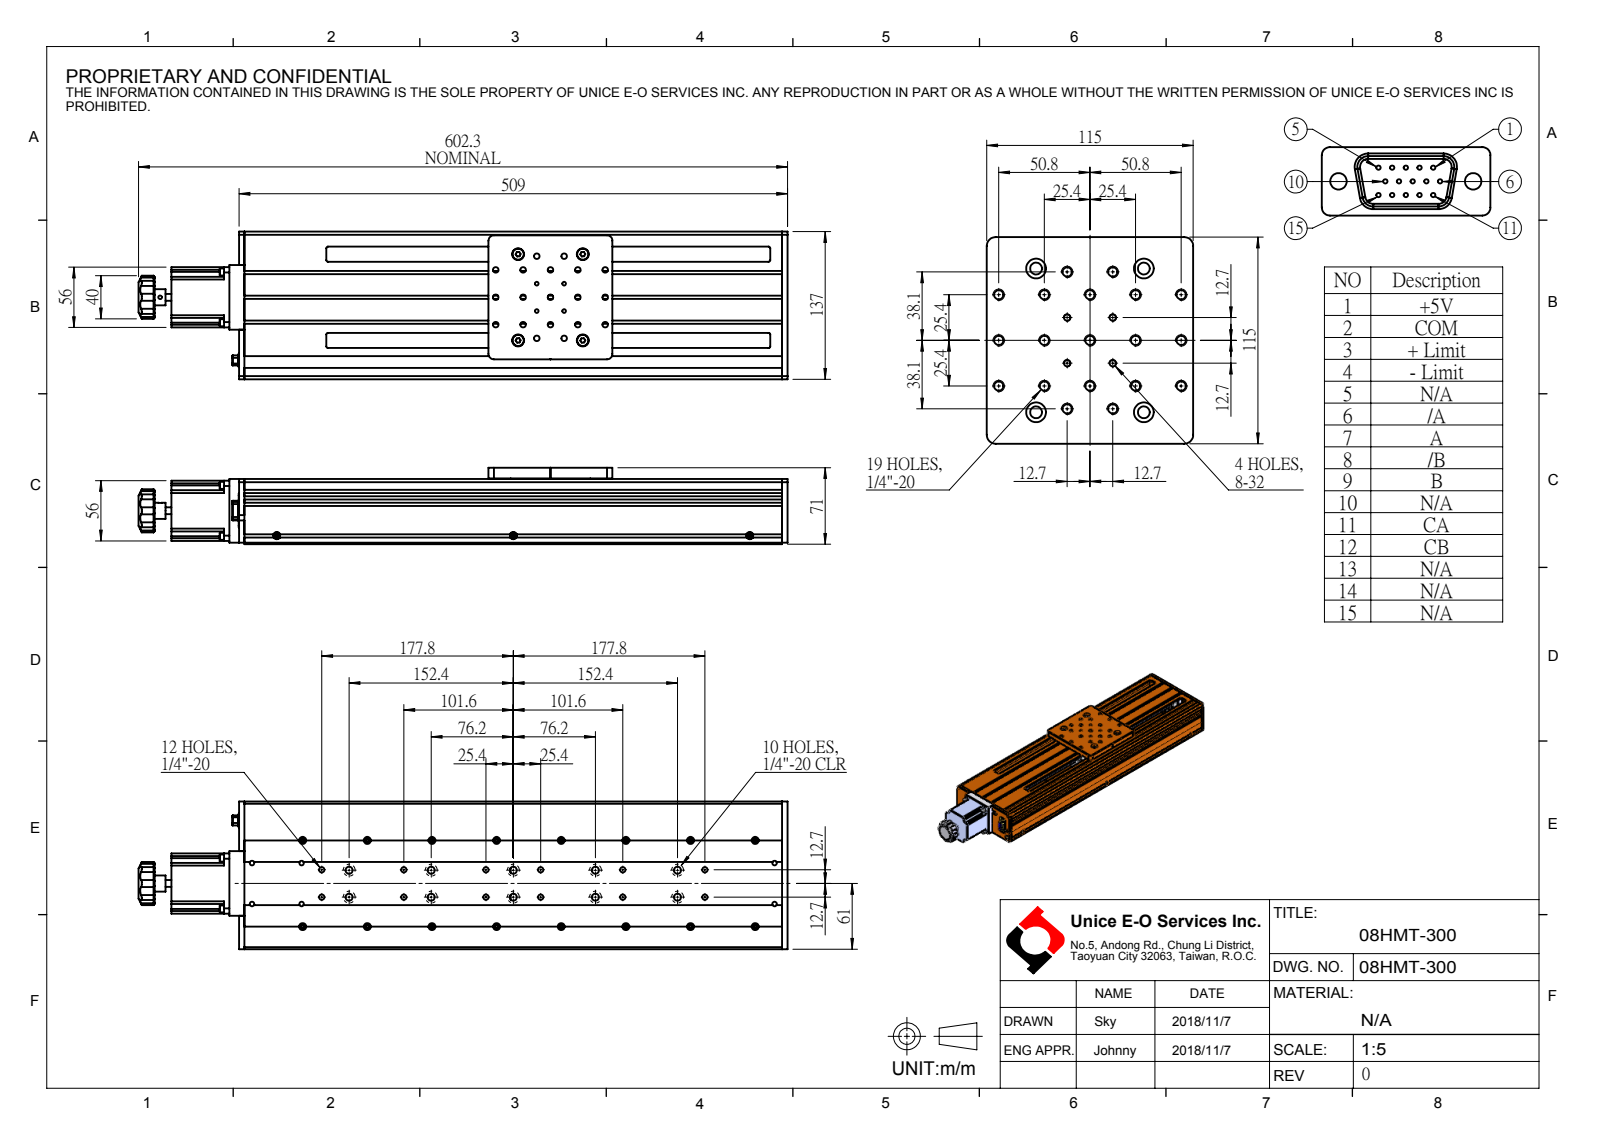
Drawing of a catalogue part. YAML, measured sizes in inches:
part_name: "08HMT-300"
step_written_by: "SolidWorks 2016 (AUTOMOTIVE_DESIGN)"
units: inches
bodies: {solids: 0, faces: 794, planar: 353, cylindrical: 316, other: 125}
overall_size: [23.713, 5.394, 2.795]
round_holes:
  - {diameter: 0.201, count: 19}
  - {diameter: 0.256, count: 16}
  - {diameter: 0.197, count: 12}
  - {diameter: 0.433, count: 12}
  - {diameter: 0.26, count: 10}
  - {diameter: 0.031, count: 8}
  - {diameter: 0.165, count: 6}
  - {diameter: 0.136, count: 4}
  - {diameter: 0.079, count: 2}
  - {diameter: 0.089, count: 2}
  - {diameter: 0.12, count: 2}
  - {diameter: 0.13, count: 2}
round_bosses_or_shafts:
  - {diameter: 0.256, count: 4}
  - {diameter: 0.228, count: 3}
  - {diameter: 0.303, count: 2}
  - {diameter: 0.276, count: 2}
  - {diameter: 0.591, count: 1}
  - {diameter: 0.551, count: 1}
  - {diameter: 0.25, count: 1}
partial_cylinders:
  - {radius: 0.059, count: 11}
  - {radius: 0.157, count: 8}
  - {radius: 0.197, count: 8}
  - {radius: 0.292, count: 8}
  - {radius: 0.02, count: 7}
  - {radius: 0.079, count: 4}
  - {radius: 0.177, count: 4}
  - {radius: 0.118, count: 3}
face_to_face_distances: [0.079, 2.382, 5.315, 5.236, 0.413, 0.059, 2.323, 5.394, 0.067, 0.354]
hole_center_spacings: [1.581, 1, 0.707, 2.236, 1.414, 2.55, 2, 2.121]
